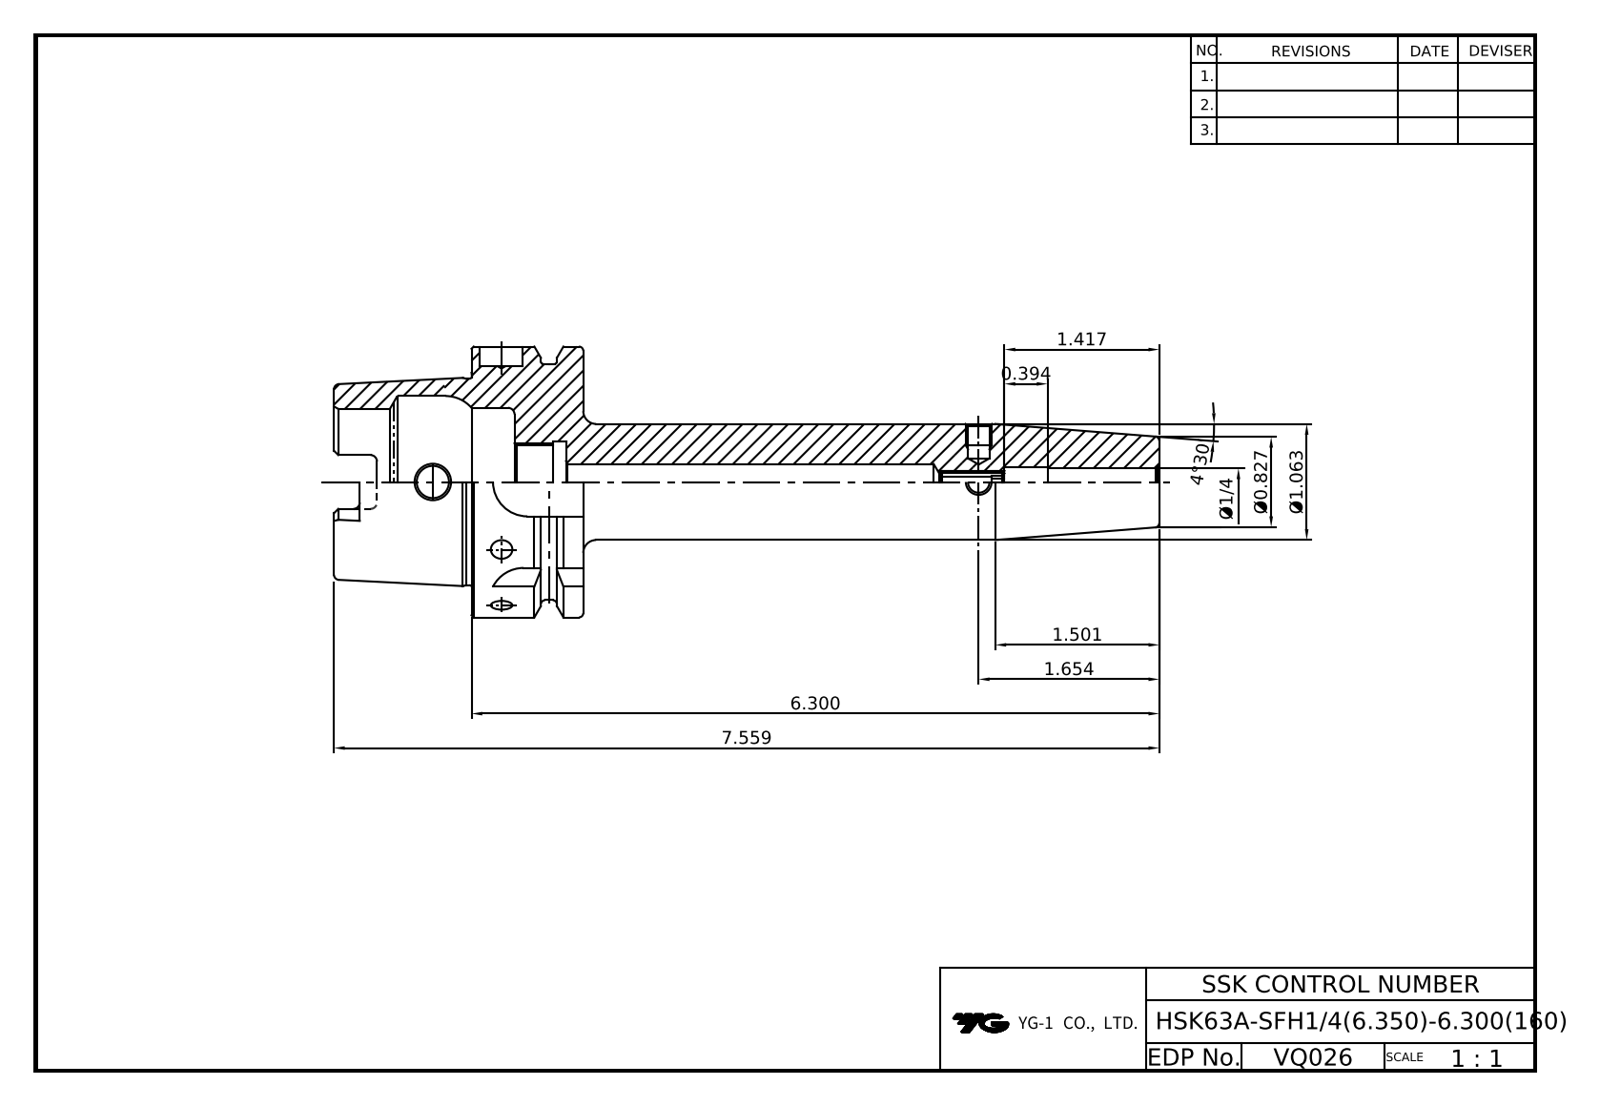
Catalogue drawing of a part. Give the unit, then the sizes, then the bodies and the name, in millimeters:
Units: millimetres
Overall size (bounding box): 192 × 63 × 63
Round holes (diameter × count): ⌀4.3 ×1, ⌀6.35 ×1, ⌀7.5 ×1, ⌀7.55 ×1, ⌀8.4 ×1, ⌀10 ×1, ⌀16.92 ×1, ⌀19 ×1, ⌀34 ×1, ⌀40 ×1
Round bosses / shafts (diameter × count): ⌀63 ×1, ⌀55 ×1, ⌀48.04 ×1, ⌀27 ×1
Partial cylindrical surfaces — rounded edges, fillets, slot ends (radius × count): R1.5 ×6, R2.88 ×4, R8 ×4
Main face-to-face distances: 26, 10, 16, 32, 42, 58, 53, 22, 4, 150
Volume: 147 788 mm³ · Surface area: 36 165 mm²
Bodies: 1 solid, 116 faces (42 planar, 34 cylindrical, 40 other)
Part name (STEP PRODUCT): LO-HSK63A-SFH6.35-160
STEP written by: Autodesk Inventor 2022 (AUTOMOTIVE_DESIGN)
